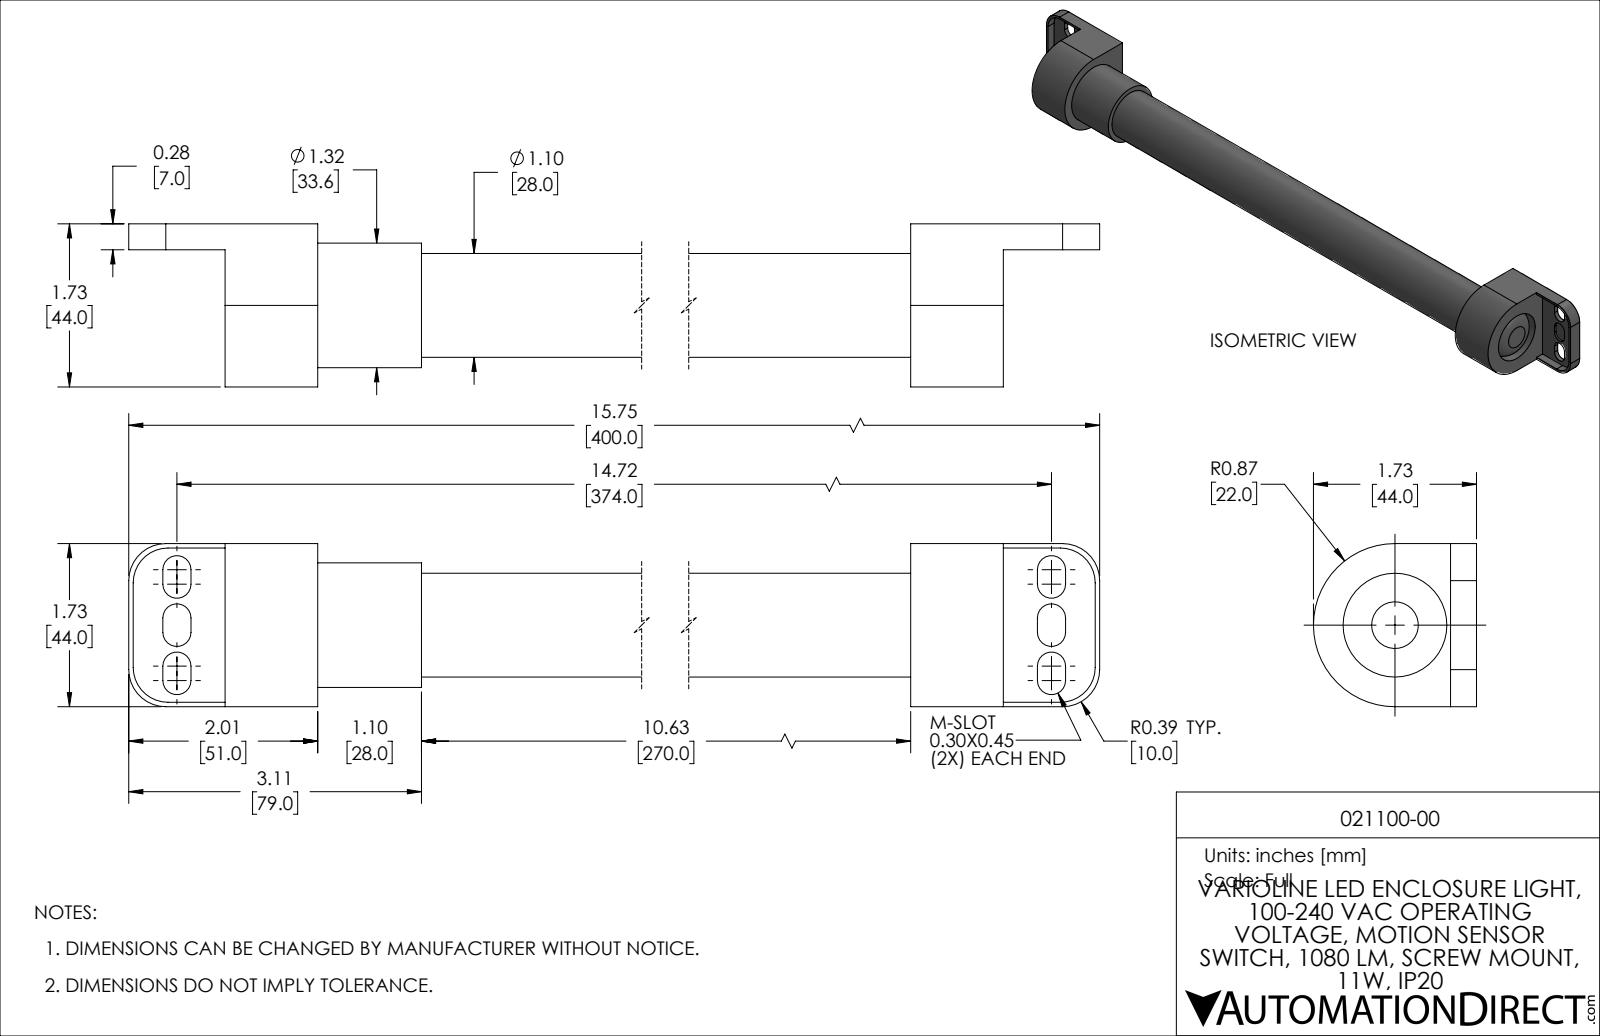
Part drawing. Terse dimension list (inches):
name: PRODUCT_NAME_1
written by: ACIS (AUTOMOTIVE_DESIGN_CC2)
unit: in
bodies: 1 solid, 73 faces (39 planar, 30 cylindrical, 4 other)
size: 15.748 × 1.732 × 1.732
volume: 17.14 in³; area: 74.8 in²
holes: 1× ⌀1.102
bosses: 1× ⌀1.323
rounds: 12× R0.15, 4× R0.37, 4× R0.394, 1× R0.866
face distances: 0.984, 12.717, 0.094, 1.732, 13.701, 11.732, 0.047, 14.724, 1.024, 2.008
